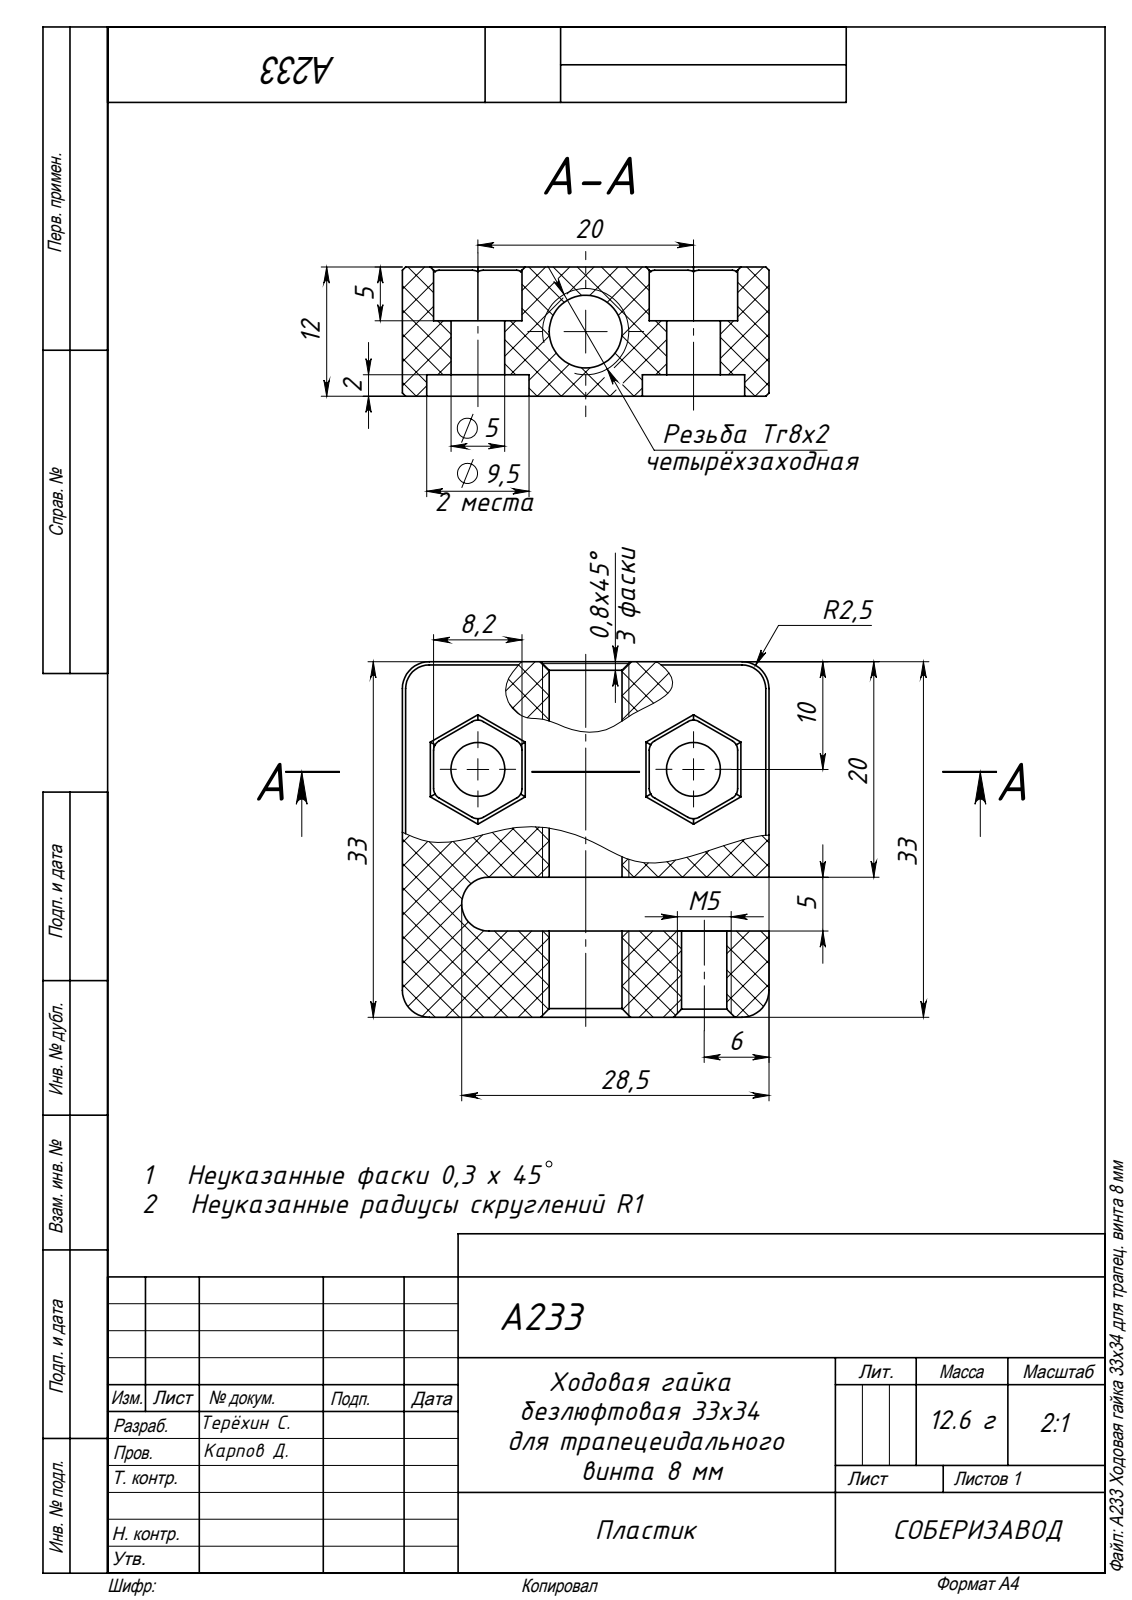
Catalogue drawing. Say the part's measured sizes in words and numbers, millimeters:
The part is named "A233 Ходовая гайка 33x34 для трапец. винта 8 мм". Its 3-D file was written by "SolidWorks 2019 (AUTOMOTIVE_DESIGN)". It is 1 solid with 100 faces: 51 planar, 32 cylindrical and 17 other. Overall it measures 34 by 33 by 12 millimeters. Its volume is 9 512 cubic millimeters and its surface area 5 074 square millimeters. Round holes: 2 of diameter 5, 2 of diameter 9.5, 1 of diameter 4.2, 1 of diameter 6.75. Partial cylindrical surfaces (rounded edges, fillets, slot ends): 12 of radius 1, 5 of radius 2.5. The main face-to-face distances are 12, 5, 20, 34, 13, 33, 8, 25, 10, 2. The hole center spacings are 11, 20.
